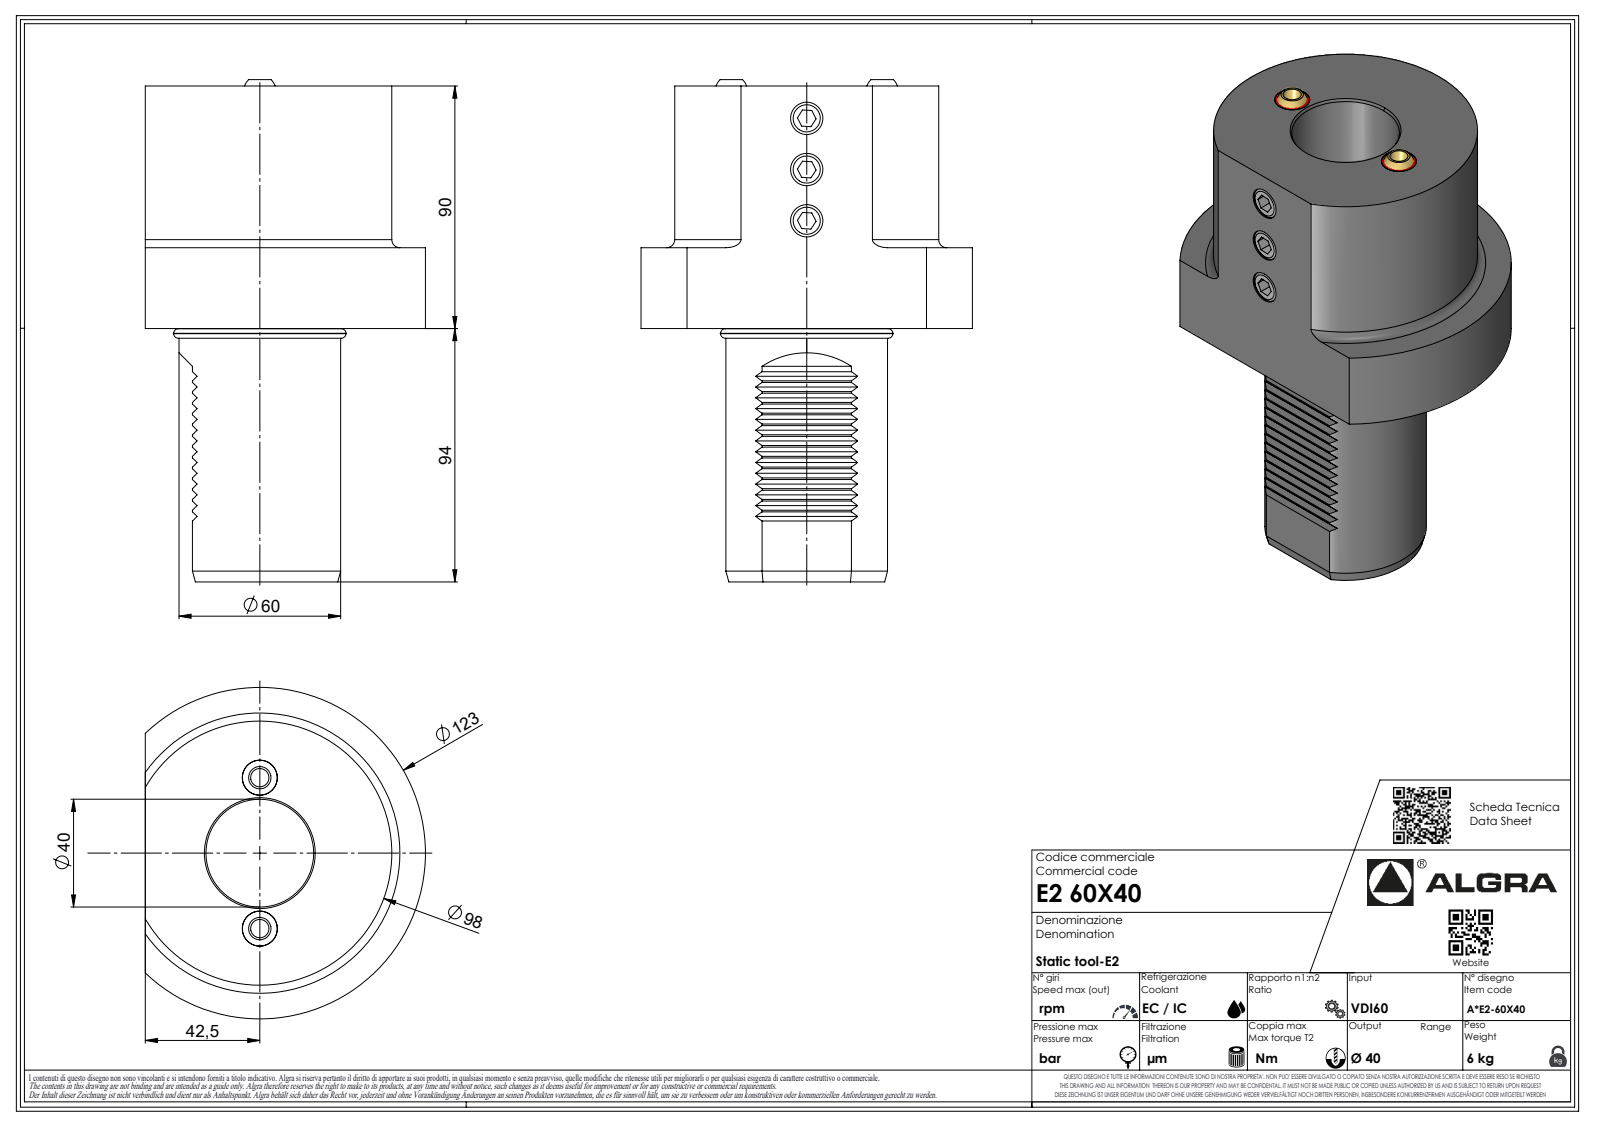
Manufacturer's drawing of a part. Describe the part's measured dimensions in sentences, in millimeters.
The part is named "E260X40". Its 3-D file was written by "SolidWorks 2023 (AUTOMOTIVE_DESIGN)". It is 1 solid with 275 faces: 199 planar, 32 cylindrical and 44 other. Overall it measures 186.37 by 123 by 104 millimeters. Its volume is 1 012 000 cubic millimeters and its surface area 70 078 square millimeters. Round holes: 1 of diameter 2.1, 1 of diameter 40. Round bosses or shafts: 1 of diameter 98, 1 of diameter 64.19, 1 of diameter 60, 1 of diameter 6.37, 1 of diameter 1.7. Partial cylindrical surfaces (rounded edges, fillets, slot ends): 7 of radius 0.33, 7 of radius 0.52, 7 of radius 3.7, 1 of radius 0.21, 1 of radius 61.5. The main face-to-face distances are 90, 60, 30, 184, 124, 94, 2.83, 14.14, 11.31, 5.
